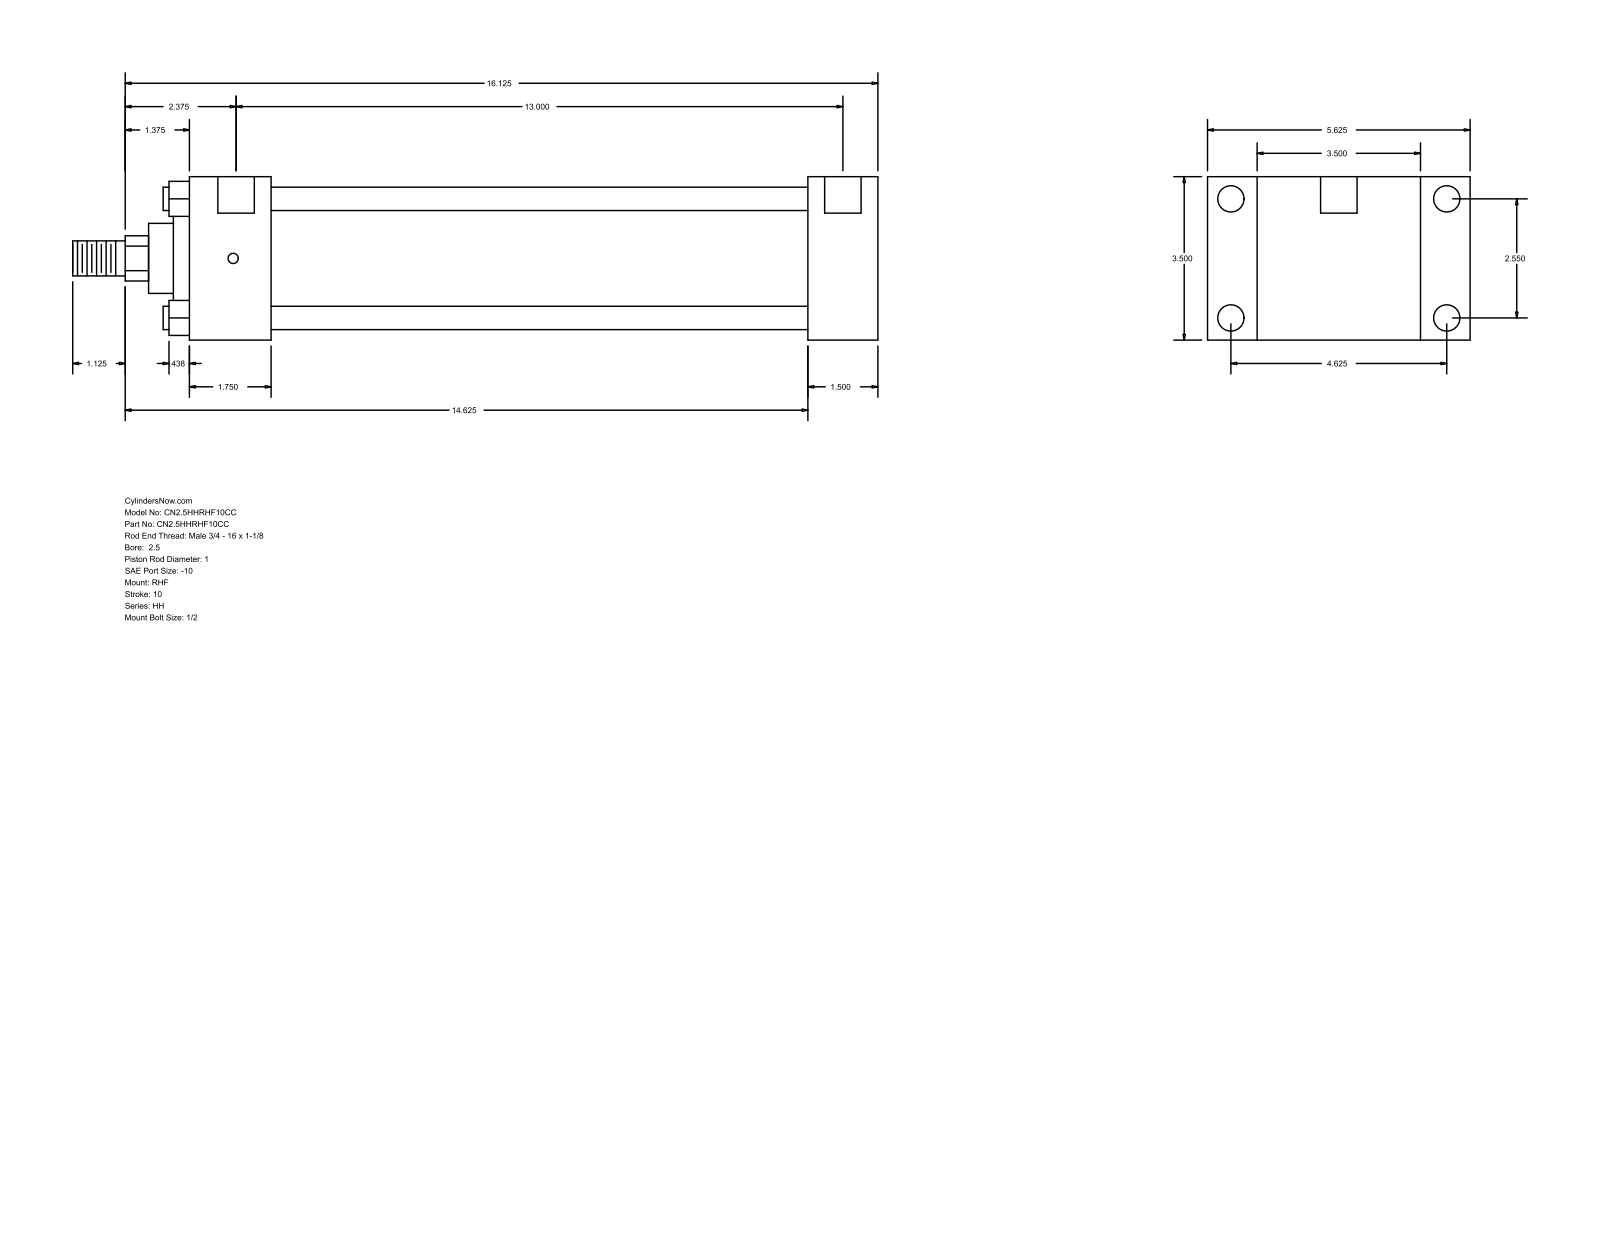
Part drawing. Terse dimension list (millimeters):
name: HH_RHF__0250_1
written by: GSSL Pune (CONFIG_CONTROL_DESIGN)
unit: mm
bodies: 0 solids, 90 faces (61 planar, 29 cylindrical, 0 other)
size: 438.15 × 142.88 × 88.9
holes: 4× ⌀5.56, 4× ⌀14.3, 2× ⌀19.84
bosses: 4× ⌀12.7, 1× ⌀73.03, 1× ⌀60.33, 1× ⌀38.1, 1× ⌀25.4, 1× ⌀19.05
rounds: 1× R12.29
face distances: 88.9, 38.09, 26.99, 115.89, 336.56, 374.65, 142.88, 44.46, 292.1, 330.19
hole spacings: 1.59, 64.76, 117.48, 134.15, 331.78, 333.37, 330.19
